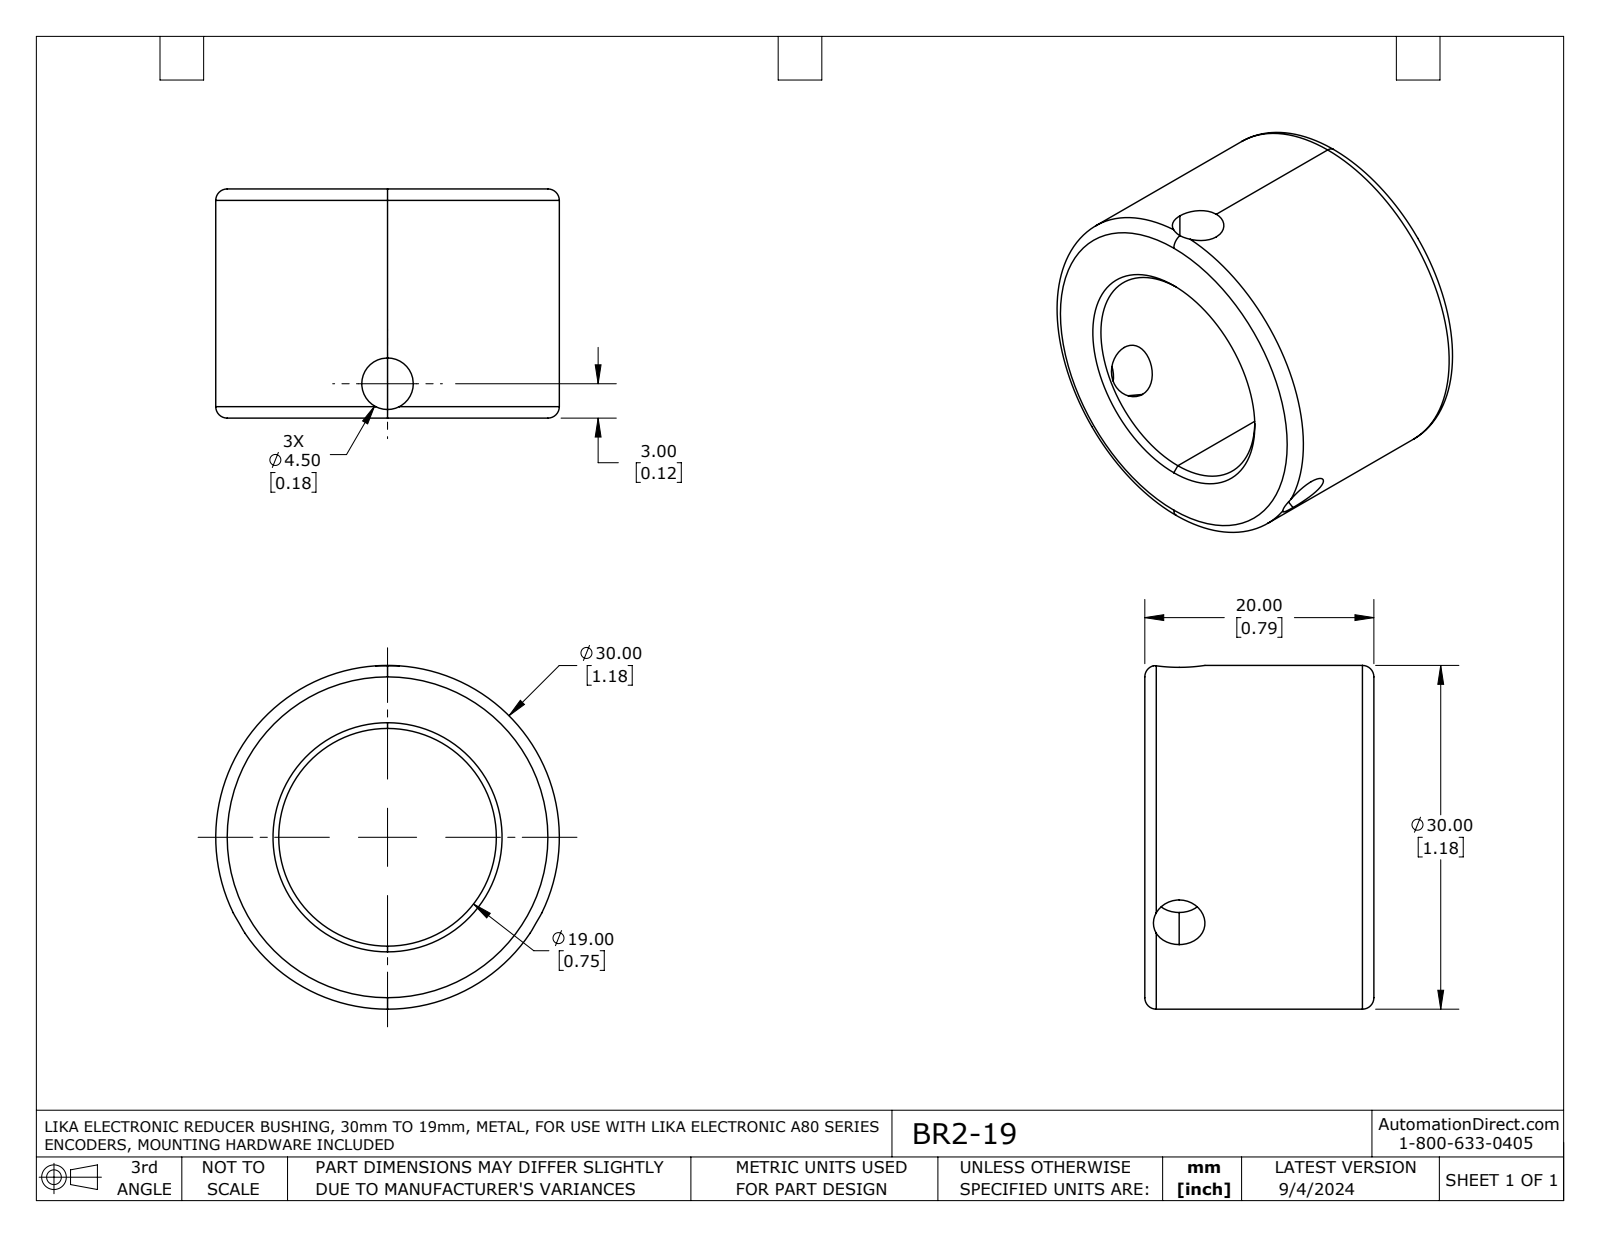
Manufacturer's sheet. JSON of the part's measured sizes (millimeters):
{"part_name": "BR2-19", "step_written_by": "SolidWorks 2021 (AUTOMOTIVE_DESIGN)", "units": "millimeters", "bodies": {"solids": 1, "faces": 25, "planar": 2, "cylindrical": 13, "other": 10}, "overall_size": [30, 30, 20], "volume_mm3": 8140, "surface_area_mm2": 3948, "round_holes": [[4.5, 3], [19, 1]], "round_bosses_or_shafts": [[30, 1]], "face_to_face_distances": [20]}
